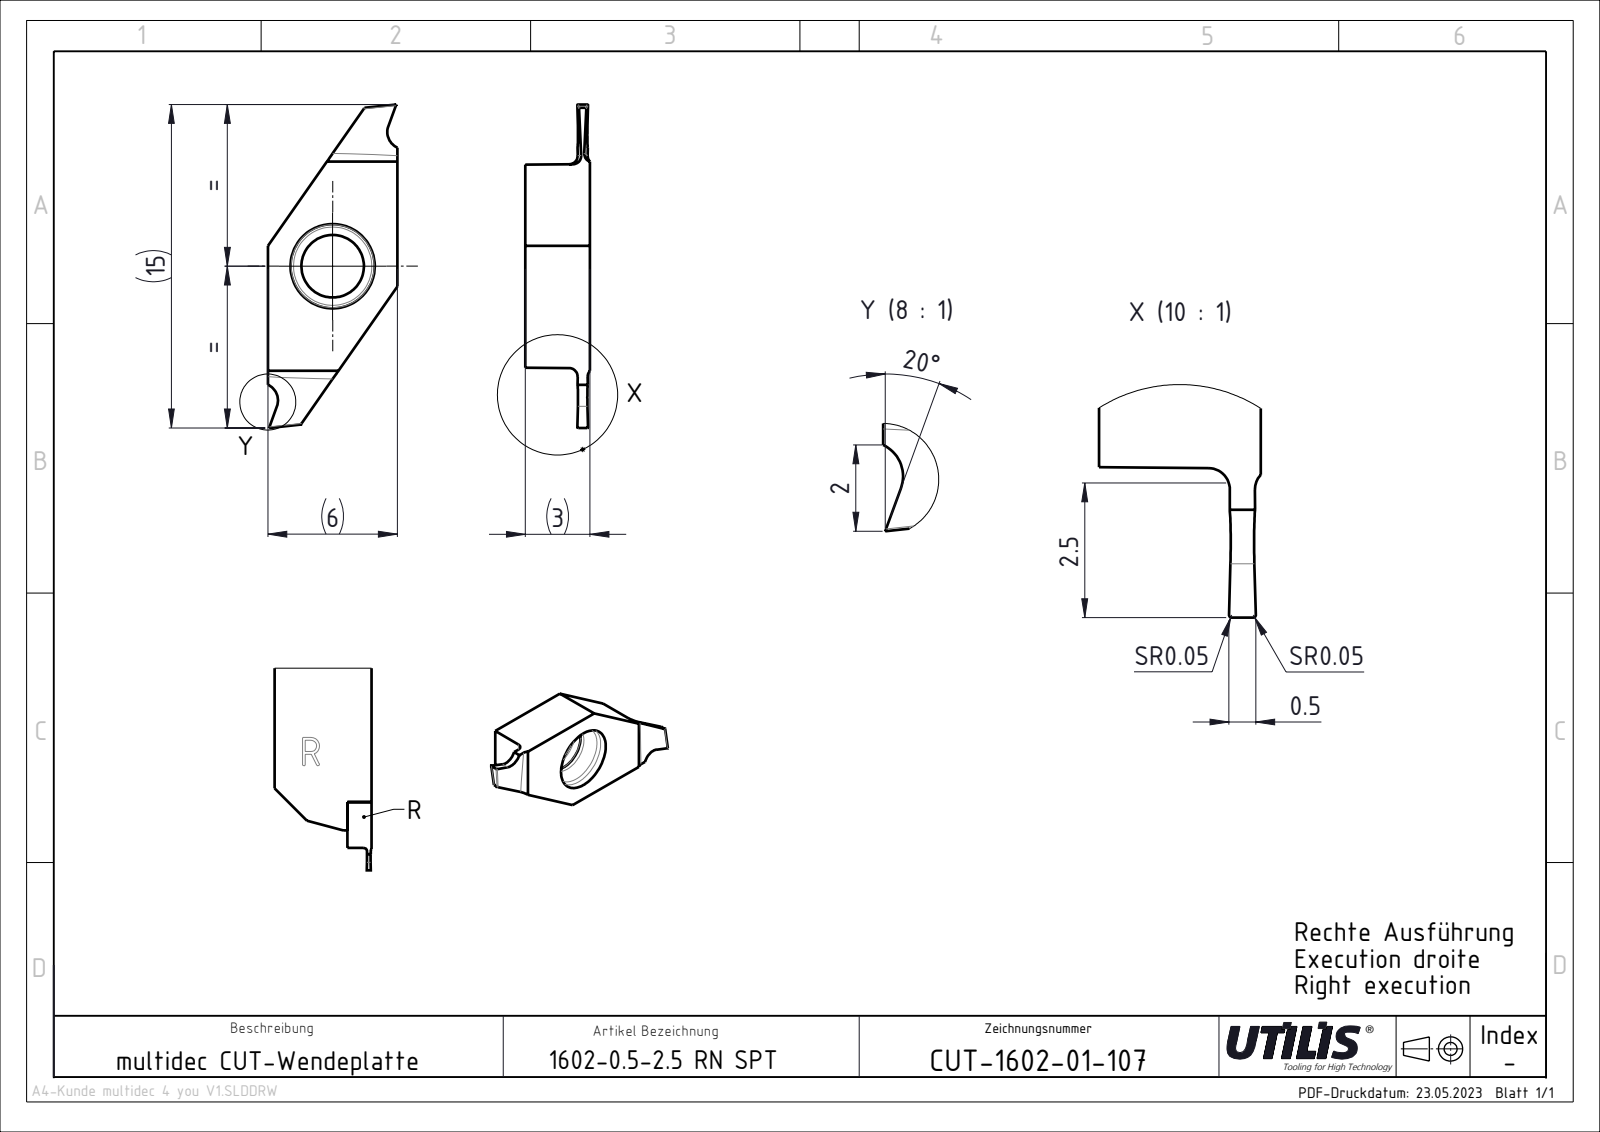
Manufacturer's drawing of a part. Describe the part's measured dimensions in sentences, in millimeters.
The part is named "1602-CUT-1602-01-107 stp". Its 3-D file was written by "SolidWorks 2022 (AUTOMOTIVE_DESIGN)". It is 1 solid with 23 faces: 14 planar, 9 cylindrical and 0 other. Overall it measures 15 by 6 by 3 millimeters. Its volume is 127 cubic millimeters and its surface area 218 square millimeters. Round holes: 1 of diameter 2.9. Partial cylindrical surfaces (rounded edges, fillets, slot ends): 4 of radius 0.4. The main face-to-face distances are 3, 6, 0.36, 15.
